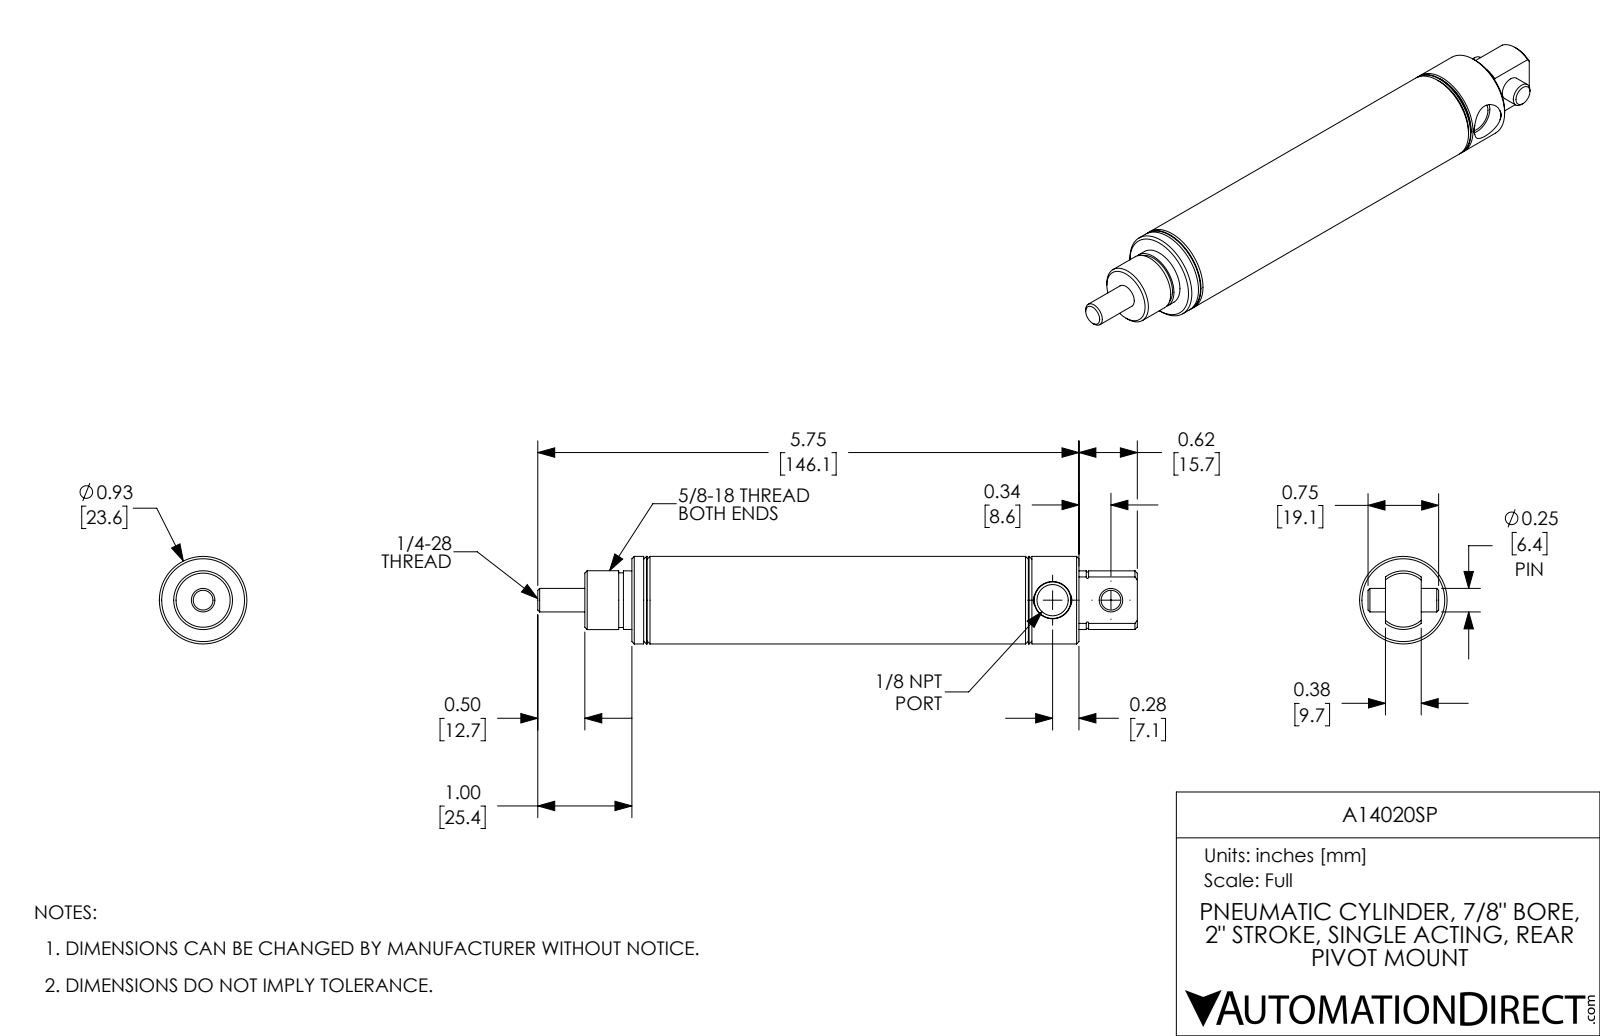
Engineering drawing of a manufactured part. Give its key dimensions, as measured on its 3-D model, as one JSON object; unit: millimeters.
{"part_name": "A14020SP; A14020SP-Pin; A14020SP-Rod; A14020SP-MainBody", "step_written_by": "SolidWorks 2017 (AUTOMOTIVE_DESIGN)", "units": "millimeters", "bodies": {"solids": 3, "faces": 87, "planar": 20, "cylindrical": 34, "other": 33}, "overall_size": [161.8, 23.6, 23.6], "volume_mm3": 39510, "surface_area_mm2": 21750, "round_holes": [[6.4, 2], [8.4, 1], [22.2, 1]], "round_bosses_or_shafts": [[23.6, 1], [15.9, 1], [15.8, 1], [14.7, 1]], "face_to_face_distances": [12.7, 63.5, 50.8, 87.3, 33.4, 120.7, 46.1, 96.9, 74.6, 23.8], "hole_center_spacings": [15.7]}
